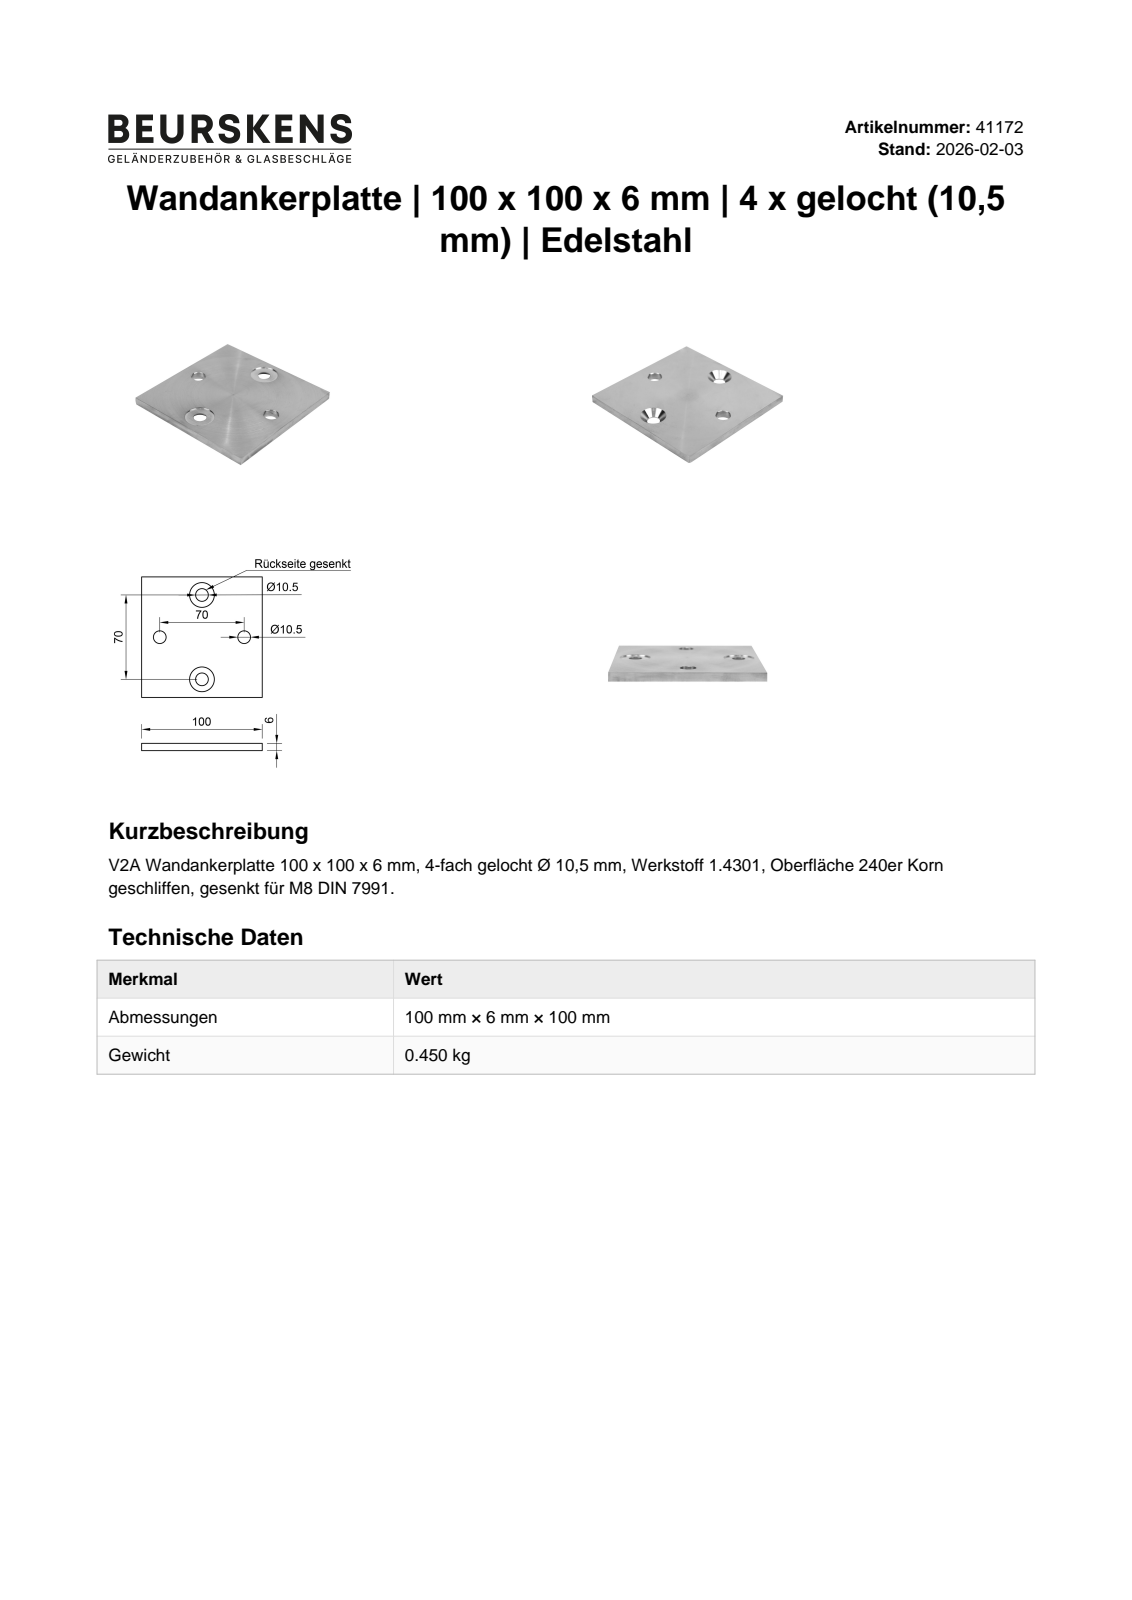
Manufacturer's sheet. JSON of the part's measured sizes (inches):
{"part_name": "41172", "step_written_by": "Autodesk Inventor 2022 (AUTOMOTIVE_DESIGN)", "units": "inches", "bodies": {"solids": 1, "faces": 16, "planar": 8, "cylindrical": 6, "other": 2}, "overall_size": [3.937, 3.937, 0.236], "volume_in3": 3.462, "surface_area_in2": 34.69, "round_holes": [[0.413, 4], [0.807, 2]], "face_to_face_distances": [0.236, 3.937, 0.228], "hole_center_spacings": [1.949, 2.756]}
